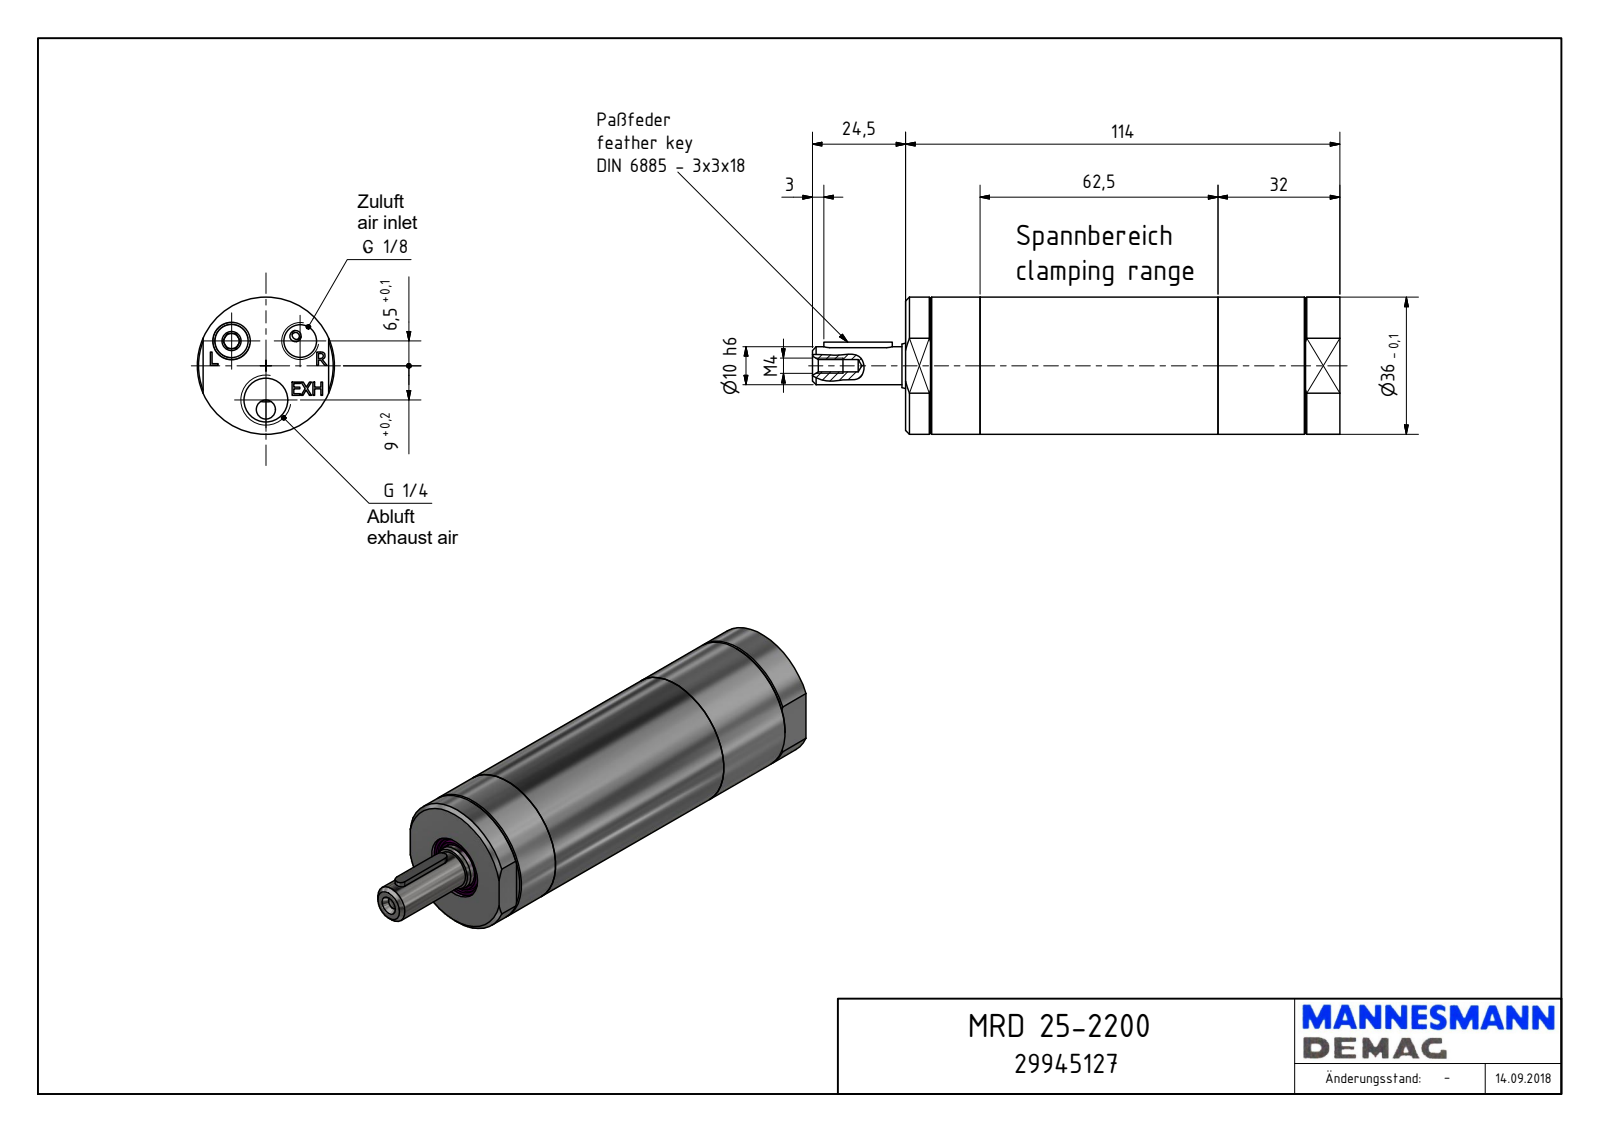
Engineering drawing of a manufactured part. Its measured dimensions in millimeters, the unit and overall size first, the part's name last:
Units: millimetres
Overall size (bounding box): 138.5 × 36 × 36
Round holes (diameter × count): ⌀8.57 ×2, ⌀3.24 ×1, ⌀4 ×1, ⌀11.45 ×1, ⌀15.5 ×1, ⌀17 ×1
Round bosses / shafts (diameter × count): ⌀36 ×1, ⌀11.95 ×1, ⌀10 ×1
Partial cylindrical surfaces — rounded edges, fillets, slot ends (radius × count): R1.5 ×2, R4 ×2, R2.5 ×1, R13.12 ×1, R15.5 ×1
Main face-to-face distances: 114, 33, 100.5, 13.5, 18, 4.5, 93.11, 7.39, 20.89, 96
Hole centre spacings: 11.1, 17.92, 9, 18
Volume: 114 292 mm³ · Surface area: 17 887 mm²
Bodies: 1 solid, 152 faces (96 planar, 25 cylindrical, 31 other)
Part name (STEP PRODUCT): MRD 25-2200_29945127
STEP written by: Autodesk Inventor 2018 (AUTOMOTIVE_DESIGN)
